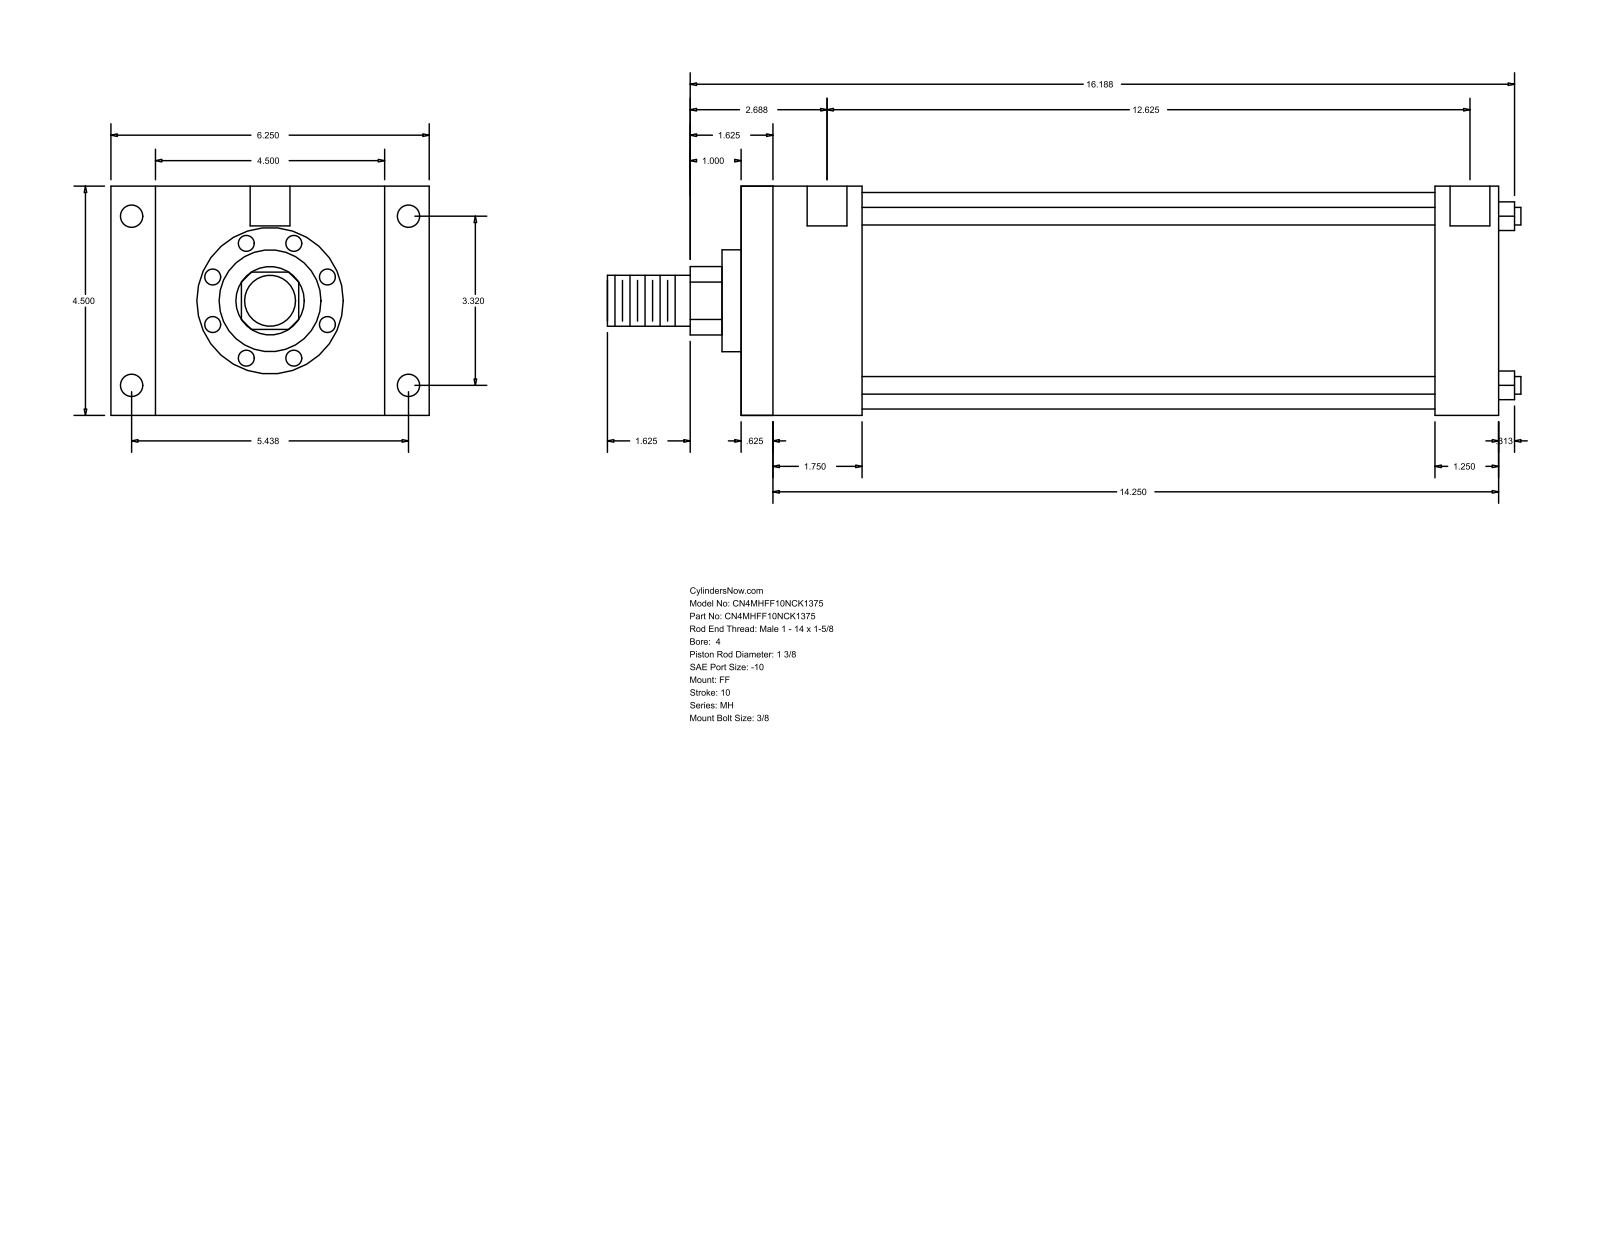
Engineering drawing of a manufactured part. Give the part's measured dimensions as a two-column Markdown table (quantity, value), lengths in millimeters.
| quantity | value |
| --- | --- |
| part name | MH_FF__0400_1.375 |
| STEP written by | GSSL Pune (CONFIG_CONTROL_DESIGN) |
| units | millimeters |
| bodies | 0 solids, 92 faces (64 planar, 28 cylindrical, 0 other) |
| overall size | 455.61 × 158.75 × 114.3 |
| round holes (diameter × count) | 8.73 × 4, 11.13 × 4, 19.84 × 2 |
| round bosses / shafts (diameter × count) | 8.76 × 4, 107.95 × 1, 50.8 × 1, 34.92 × 1, 25.4 × 1 |
| partial cylindrical surfaces (radius × count) | 17.06 × 1 |
| main face-to-face distances | 114.3, 377.83, 15.87, 361.96, 60.32, 44.45, 317.51, 346.08, 330.21, 285.76 |
| hole center spacings | 84.32, 138.12, 161.82, 323.85, 1.58, 1.59, 320.68, 322.26 |
